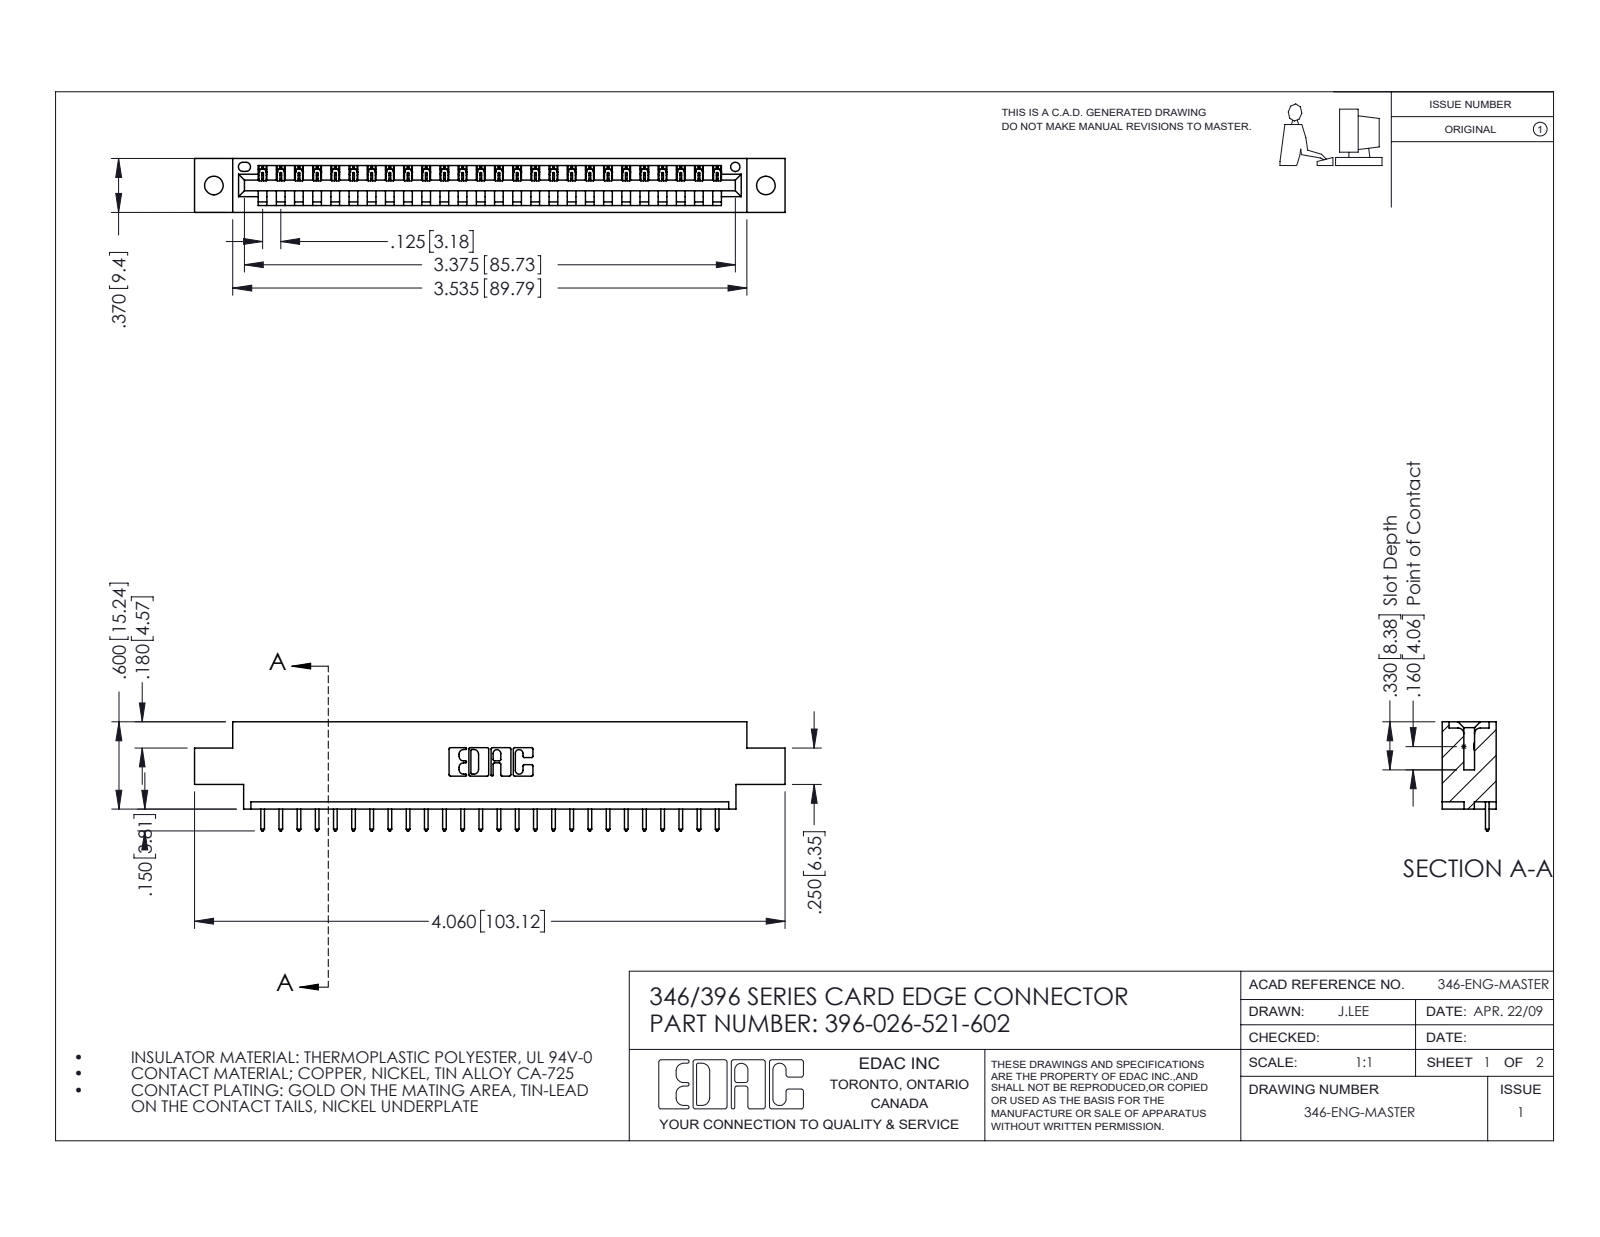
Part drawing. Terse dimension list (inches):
name: 345-292-001_345-293-121; 346 Part_0.170 Offset - 0.128 Dia; 396-026-521-602
written by: SolidWorks 2016 (CONFIG_CONTROL_DESIGN)
unit: in
bodies: 27 solids, 1634 faces (1120 planar, 514 cylindrical, 0 other)
size: 4.06 × 0.75 × 0.37
volume: 0.579 in³; area: 17.5 in²
holes: 2× ⌀0.128, 1× ⌀0.064
rounds: 52× R0.006, 52× R0.01, 22× R0.01, 6× R0.007, 6× R0.031, 3× R0.026, 2× R0.031, 2× R0.04
face distances: 0.048, 0.322, 0.37, 0.25, 0.072, 0.298, 0.025, 0.148, 0.222, 0.1
hole spacings: 0.246, 3.587, 3.795
